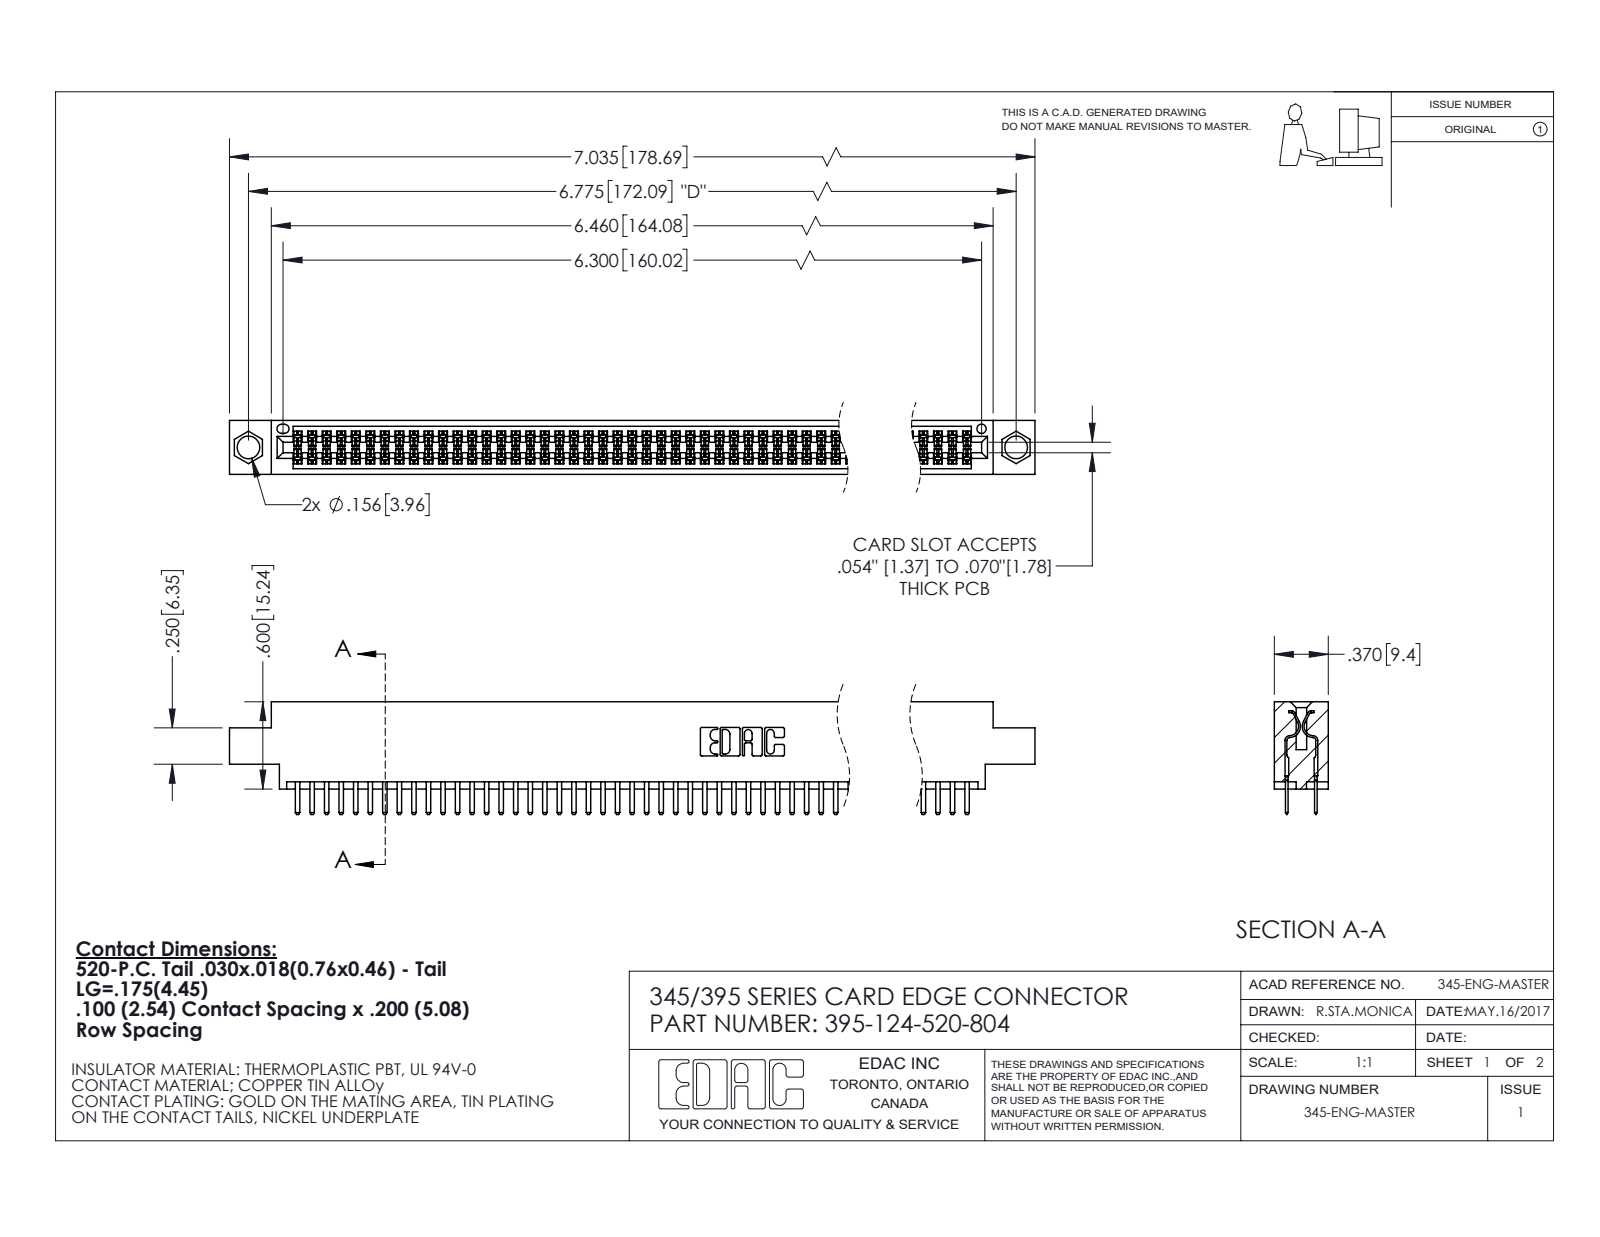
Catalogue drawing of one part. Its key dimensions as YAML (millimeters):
part_name: "345-292-001_345-293-120; 345 Part_0.170 Offset - 0.156 Dia-TI; 395-124-520-804"
step_written_by: "SolidWorks 2020 (CONFIG_CONTROL_DESIGN)"
units: millimeters
bodies: {solids: 125, faces: 6840, planar: 4438, cylindrical: 2402, other: 0}
overall_size: [178.7, 19.7, 9.4]
volume: 17270
surface_area: 25790
round_holes:
  - {diameter: 4, count: 2}
  - {diameter: 1.6, count: 1}
partial_cylinders:
  - {radius: 0.2, count: 248}
  - {radius: 0.3, count: 128}
  - {radius: 0.3, count: 22}
  - {radius: 0.2, count: 6}
  - {radius: 0.8, count: 6}
  - {radius: 0.7, count: 3}
  - {radius: 0.4, count: 2}
  - {radius: 0.5, count: 2}
face_to_face_distances: [1.8, 7.6, 5.1, 9.4, 2.5, 6.9, 0.6, 5.7, 0.6, 1.8]
hole_center_spacings: [6.9, 166.1, 172.1]
